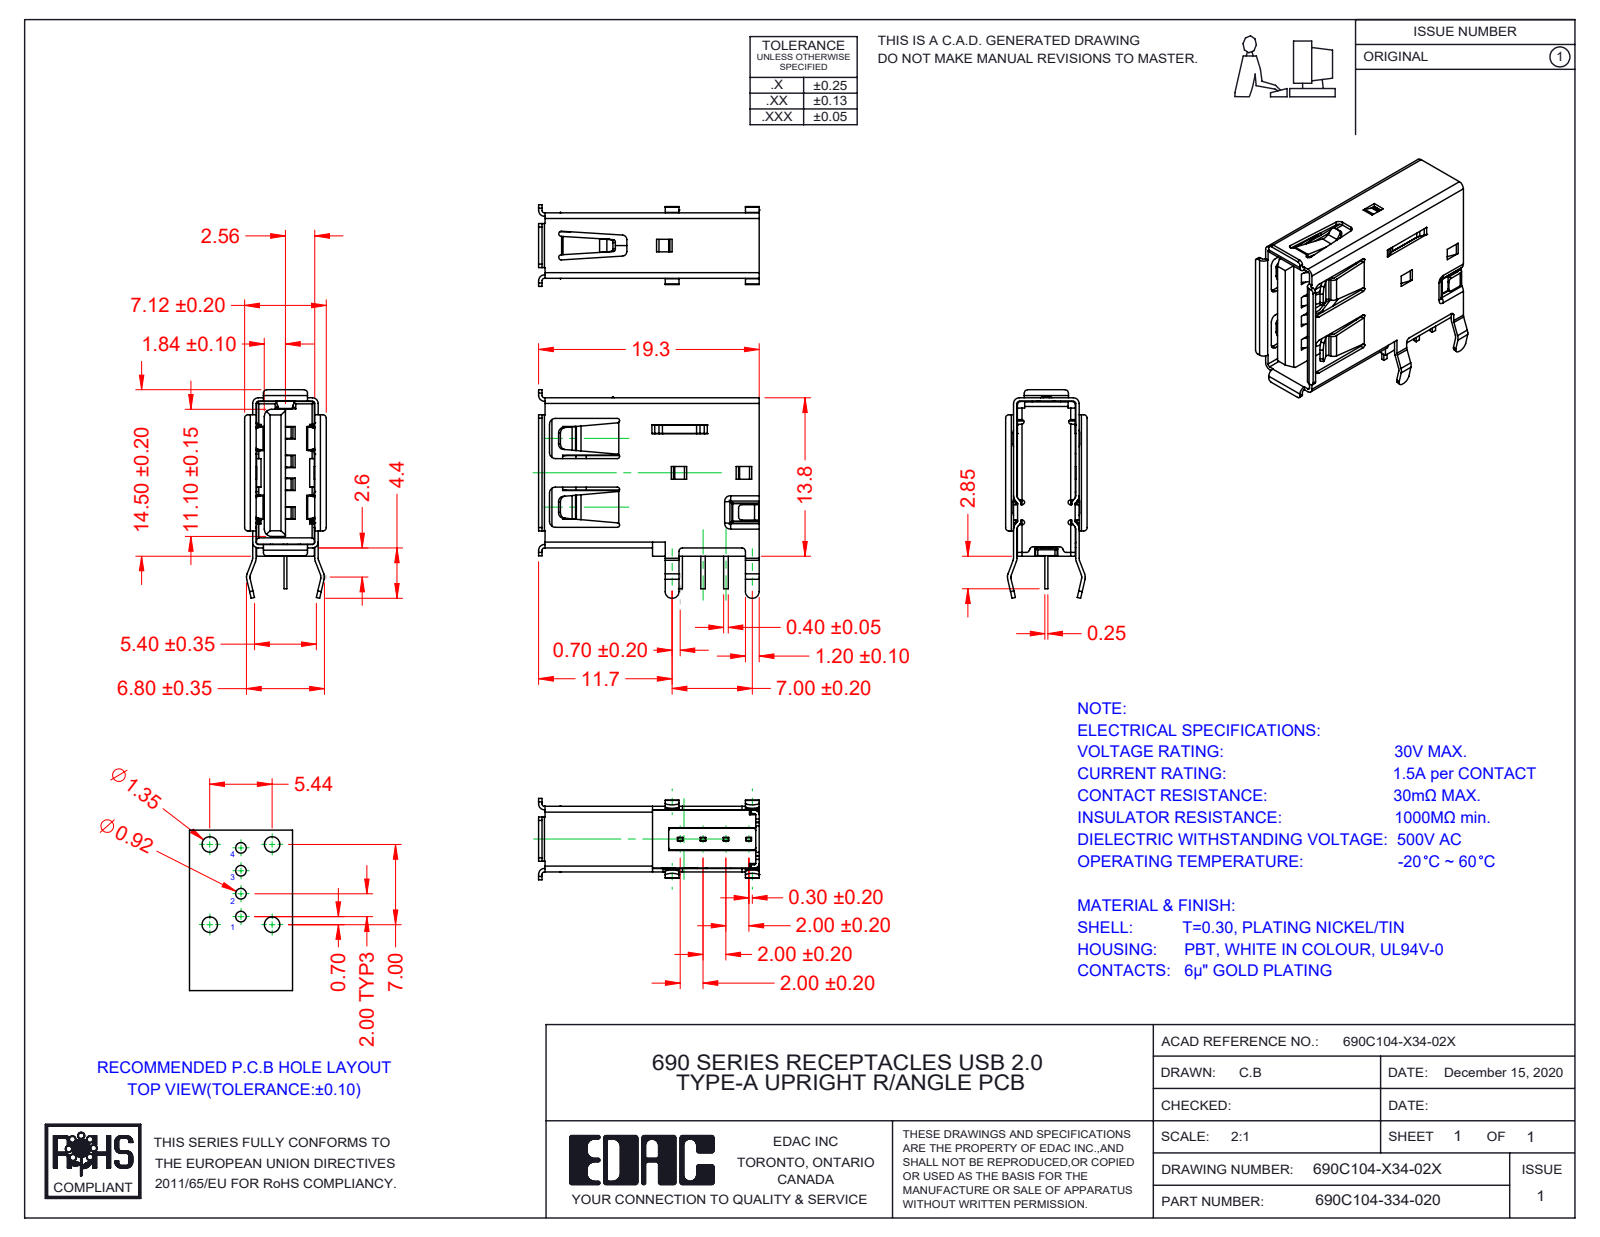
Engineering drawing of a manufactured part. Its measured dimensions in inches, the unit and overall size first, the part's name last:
Units: inches
Overall size (bounding box): 0.758 × 0.717 × 0.28
Partial cylindrical surfaces — rounded edges, fillets, slot ends (radius × count): R0.012 ×48, R0.008 ×33, R0.02 ×27, R0.016 ×24, R0.024 ×22, R0.006 ×18, R0.004 ×15, R0.028 ×11
Main face-to-face distances: 0.213, 0.225, 0.202, 0.504, 0.04, 0.113, 0.101, 0.185, 0.028, 0.098
Volume: 0.04 in³ · Surface area: 4.236 in²
Bodies: 7 solids, 1141 faces (753 planar, 332 cylindrical, 56 other)
Part name (STEP PRODUCT): Shell 690C104-X34-02X; Insulator1 690C104-X34-02X_White; Contacts_4 690C104-X34-02X; Contacts_3 690C104-X34-02X (+5 more)
STEP written by: SolidWorks 2020 (AUTOMOTIVE_DESIGN)
